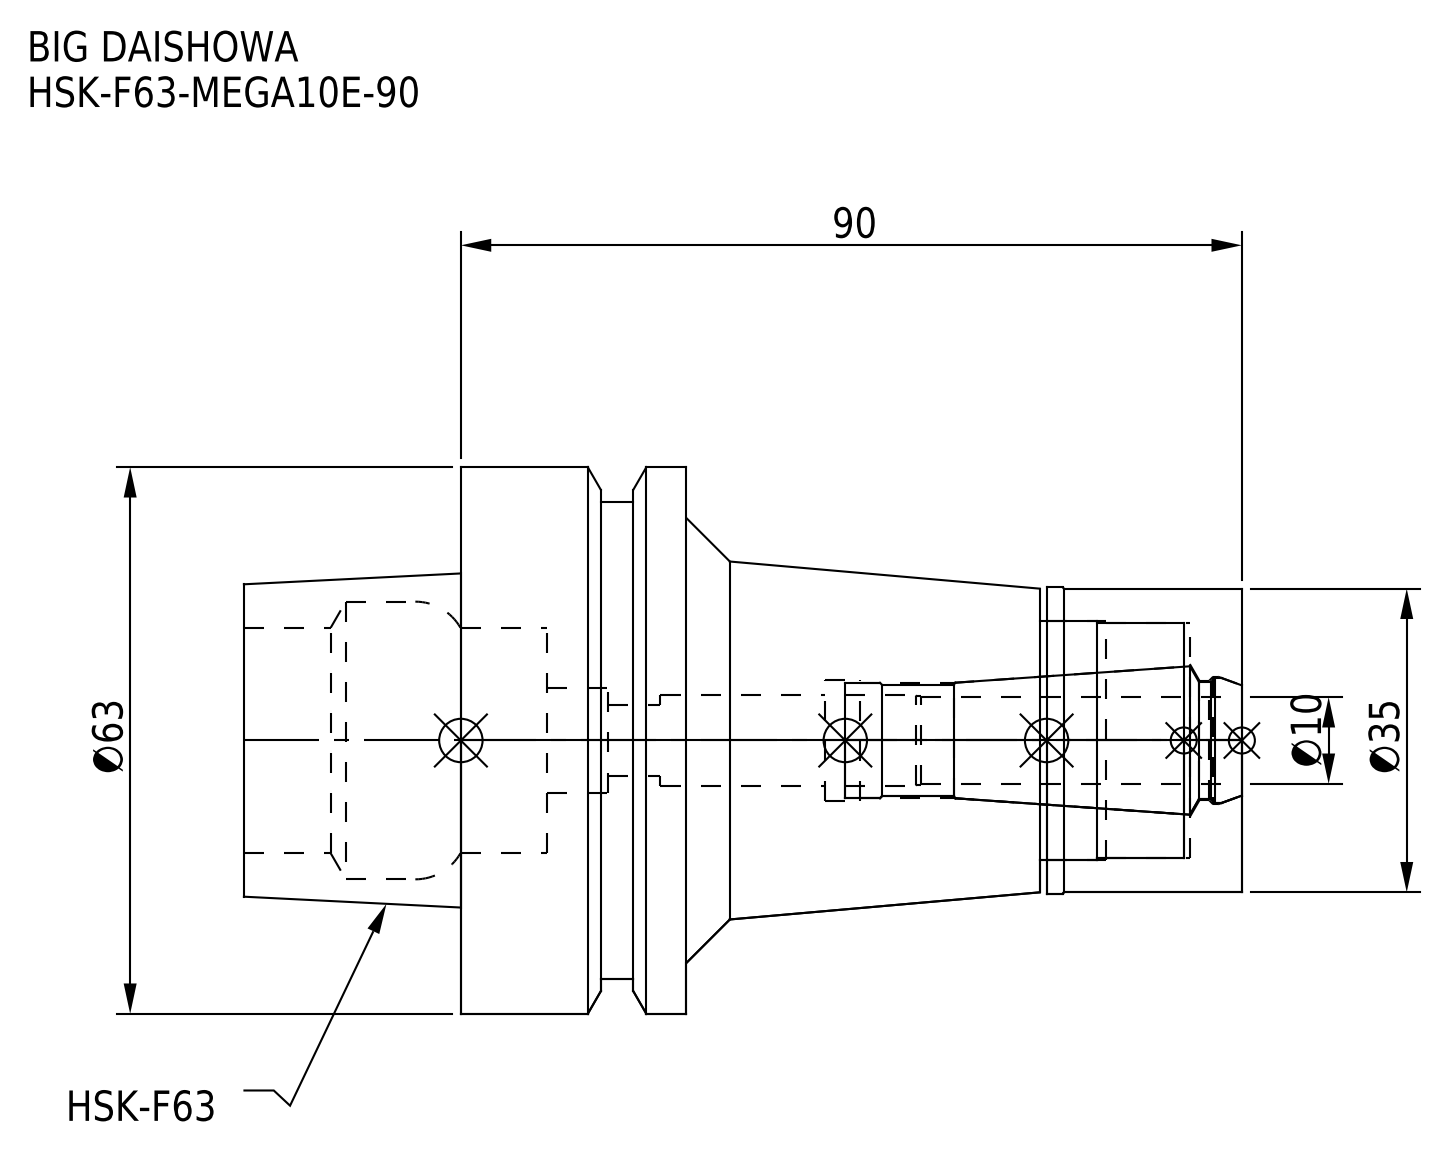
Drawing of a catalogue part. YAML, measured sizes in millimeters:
part_name: "HSK-F63-MEGA10E-90-100.stp; MEN10_1.stp; HF63ME10090-100_ASM.stp; DXF_TEMP_ASSY_ASM_4_ASM.stp (+3 more)"
step_written_by: "SolidWorks 2019 (CONFIG_CONTROL_DESIGN)"
units: millimeters
bodies: {solids: 2, faces: 81, planar: 17, cylindrical: 40, other: 24}
overall_size: [115, 63, 63]
volume: 143219
surface_area: 32657
round_holes:
  - {diameter: 8.25, count: 1}
  - {diameter: 10.4, count: 1}
  - {diameter: 12, count: 1}
  - {diameter: 13.3, count: 1}
  - {diameter: 13.8, count: 1}
  - {diameter: 13.9, count: 1}
  - {diameter: 14.7, count: 1}
  - {diameter: 26, count: 1}
  - {diameter: 27, count: 1}
  - {diameter: 27.5, count: 1}
  - {diameter: 32, count: 1}
round_bosses_or_shafts:
  - {diameter: 63, count: 1}
  - {diameter: 55, count: 1}
  - {diameter: 35.3, count: 1}
  - {diameter: 35, count: 1}
face_to_face_distances: [26, 64, 90, 115, 51, 25, 80.05, 16.05, 9.95, 34.95]
